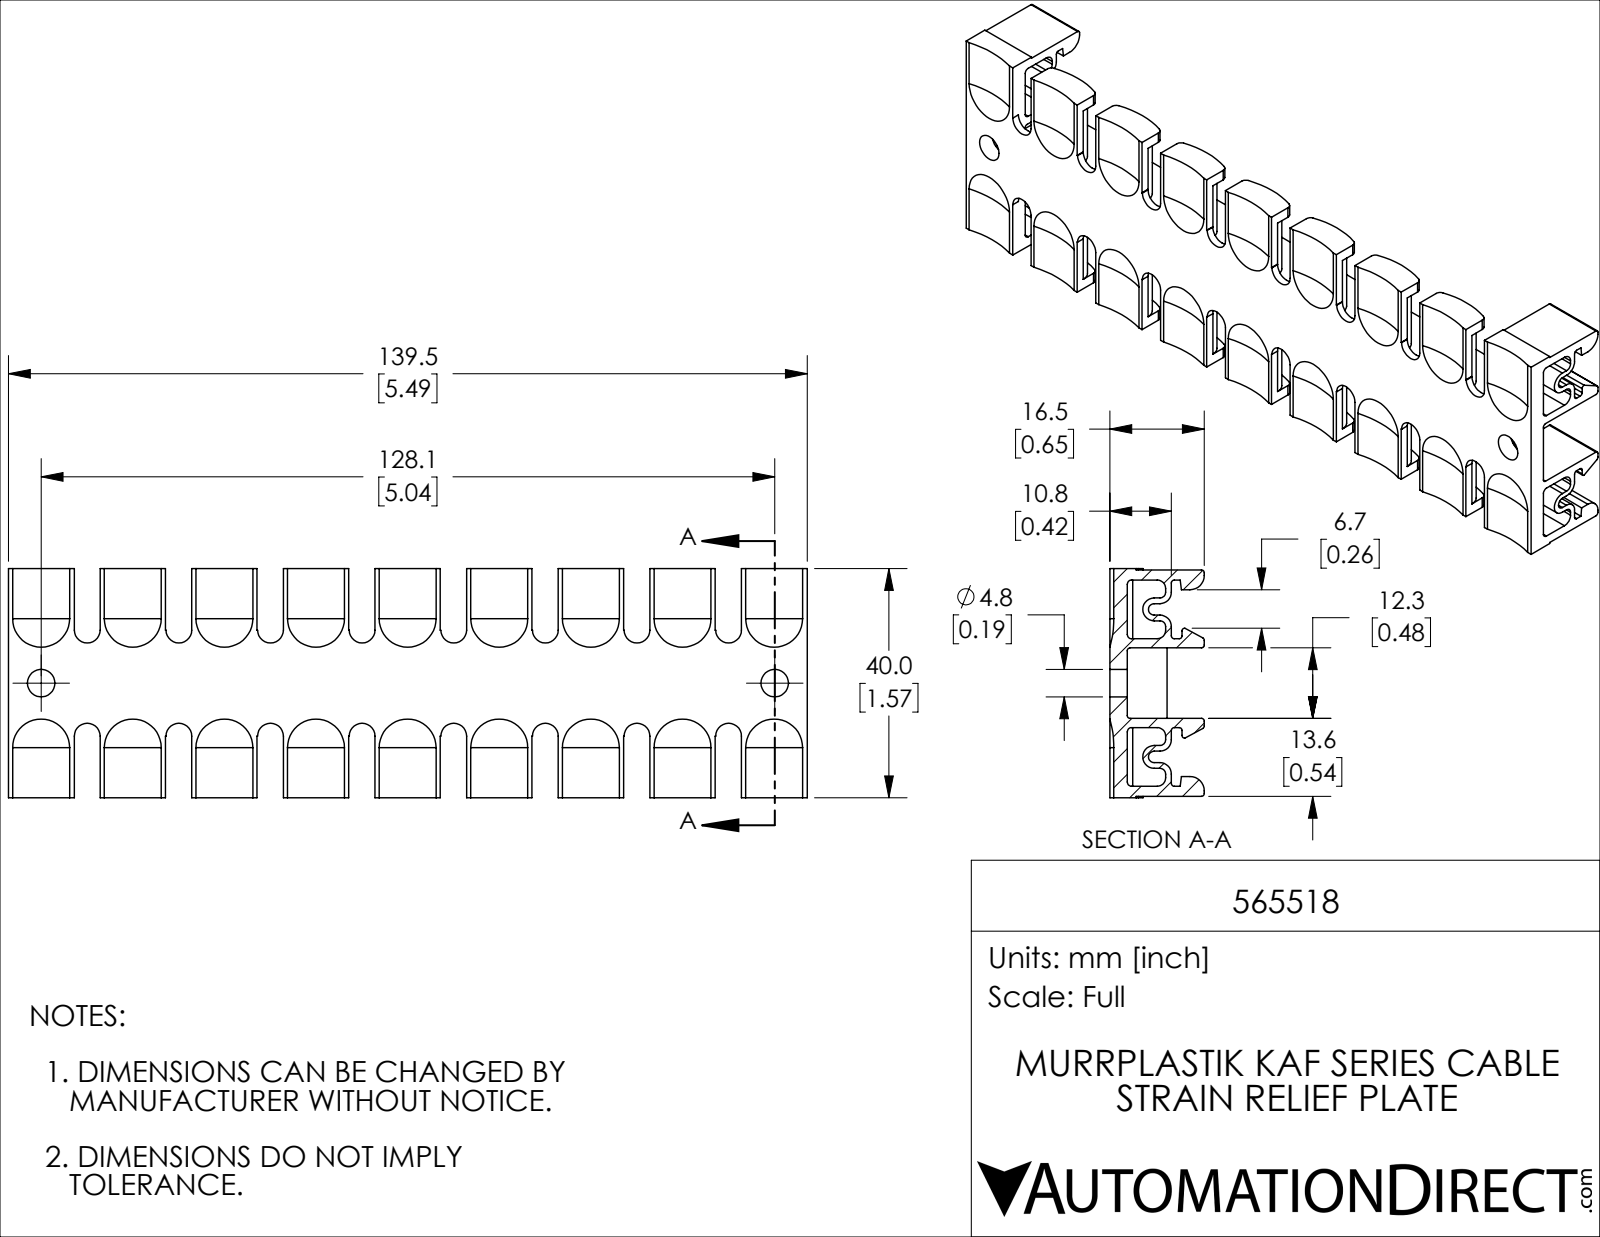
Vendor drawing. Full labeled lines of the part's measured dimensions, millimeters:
Part name (STEP PRODUCT): 565518
STEP written by: SolidWorks 2019 (CONFIG_CONTROL_DESIGN)
Units: millimetres
Bodies: 1 solid, 487 faces (240 planar, 229 cylindrical, 18 other)
Overall size (bounding box): 139.5 × 40 × 16.5
Volume: 21 243 mm³ · Surface area: 20 791 mm²
Round holes (diameter × count): ⌀4.8 ×2
Partial cylindrical surfaces — rounded edges, fillets, slot ends (radius × count): R0.5 ×32, R1 ×20, R2.25 ×16, R2.5 ×16, R18 ×9, R16 ×7, R2 ×6, R0.75 ×4
Main face-to-face distances: 11.5, 2.5, 13, 1.65, 15.5, 2.6, 1.4, 24.5, 27, 4
Hole centre spacings: 128.1
